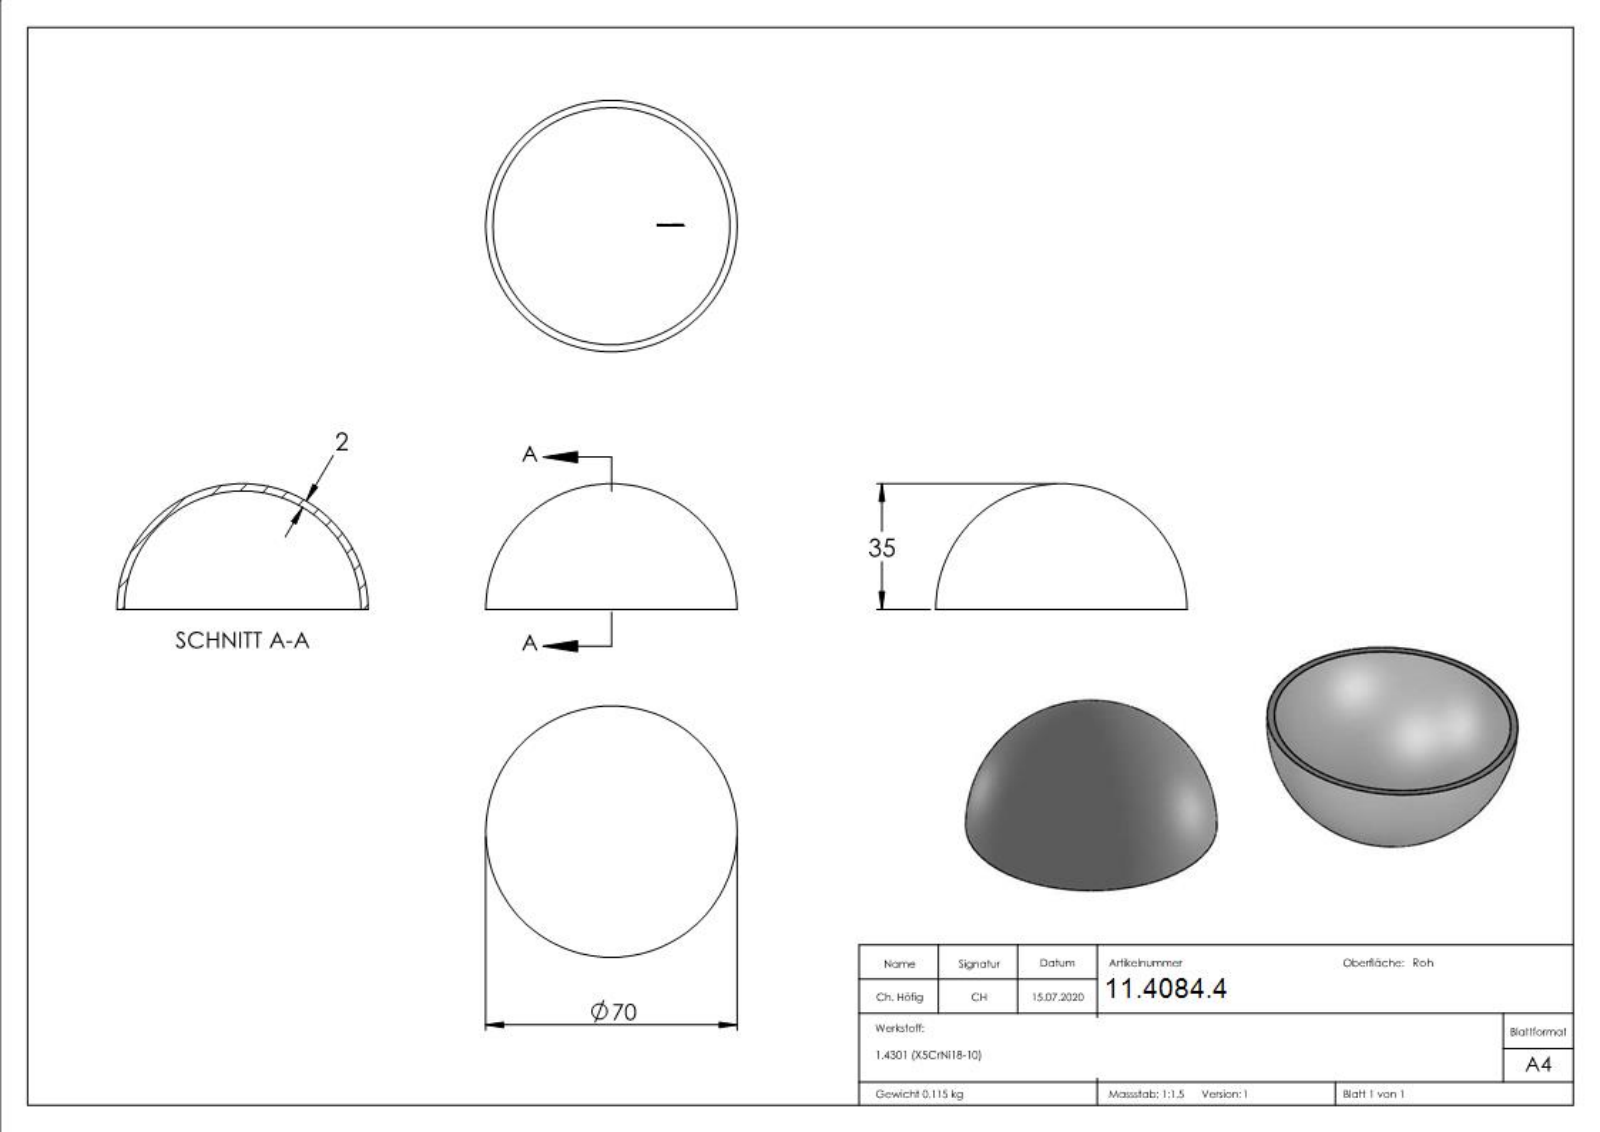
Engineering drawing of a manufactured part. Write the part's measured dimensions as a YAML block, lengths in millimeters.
part_name: "620070-VA"
step_written_by: "SolidWorks 2018 (CONFIG_CONTROL_DESIGN)"
units: millimeters
bodies: {solids: 1, faces: 209, planar: 92, cylindrical: 0, other: 117}
overall_size: [70, 70, 35]
volume: 14531
surface_area: 14971
face_to_face_distances: [0.45, 0.53, 0.5, 0.61, 1.19, 0.55, 0.81, 0.31, 1.31, 0.85]
